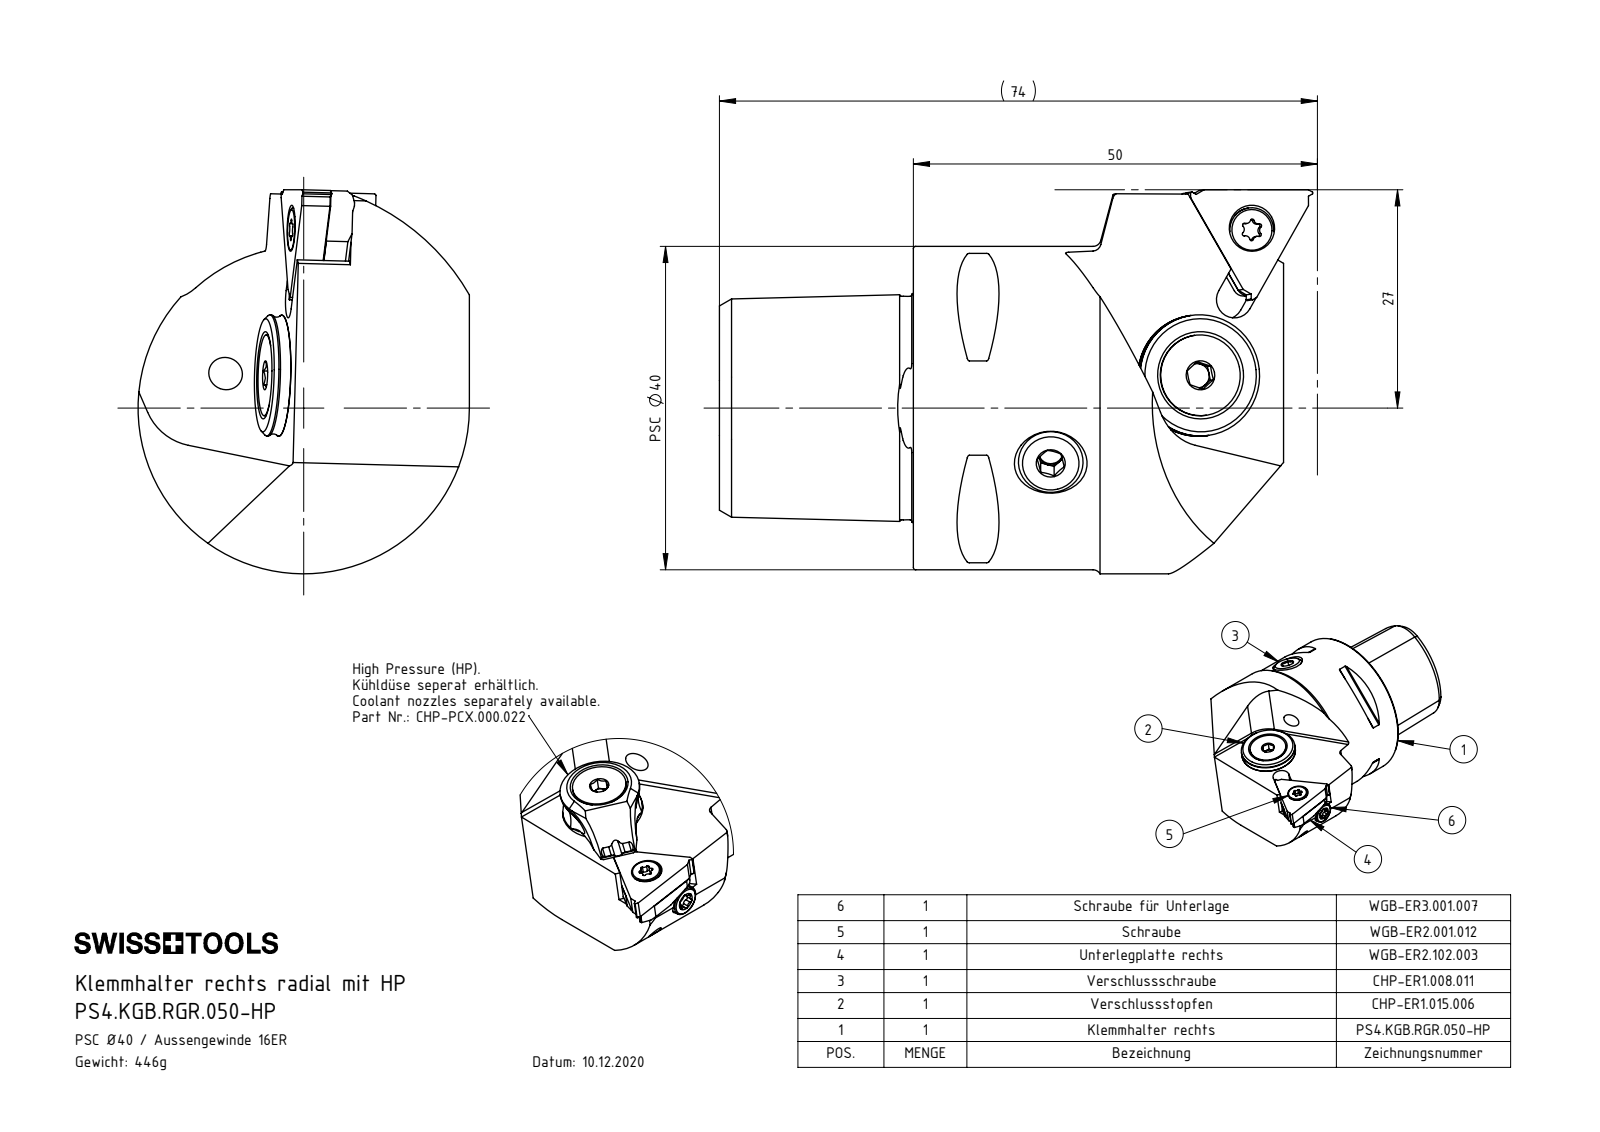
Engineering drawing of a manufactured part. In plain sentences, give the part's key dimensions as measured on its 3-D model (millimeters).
The part is named "PS4-KGB.RGR.050-HP_B; PS4.KGB.RGR.050-HP; DIN 7991 - M5x15; WGB-ER3.001.007_A (+8 more)". Its 3-D file was written by "SolidWorks 2017 (AUTOMOTIVE_DESIGN)". It is 10 solids with 316 faces: 127 planar, 83 cylindrical and 106 other. Overall it measures 73.41 by 47.5 by 41 millimeters. Its volume is 56 386 cubic millimeters and its surface area 16 455 square millimeters. Round holes: 4 of diameter 4.2, 2 of diameter 2.58, 2 of diameter 4, 1 of diameter 1.2, 1 of diameter 2, 1 of diameter 2.5, 1 of diameter 3, 1 of diameter 4.02, 1 of diameter 4.6, 1 of diameter 5.2, 1 of diameter 7, 1 of diameter 12.5. Round bosses or shafts: 3 of diameter 5.5, 1 of diameter 40, 1 of diameter 15, 1 of diameter 13.4, 1 of diameter 10, 1 of diameter 8, 1 of diameter 5, 1 of diameter 3.18. Partial cylindrical surfaces (rounded edges, fillets, slot ends): 8 of radius 0.3, 6 of radius 0.23, 6 of radius 0.34, 6 of radius 0.57, 6 of radius 0.57, 2 of radius 0.1, 2 of radius 0.5, 1 of radius 0.25. The main face-to-face distances are 4.5, 1.16, 3.34, 24, 15.52, 4.81, 3.65, 0.31, 2.07, 3.23. The hole center spacings are 4.51, 4.5, 4.52, 15.37, 15.39, 15.54, 15.56, 19.29.
